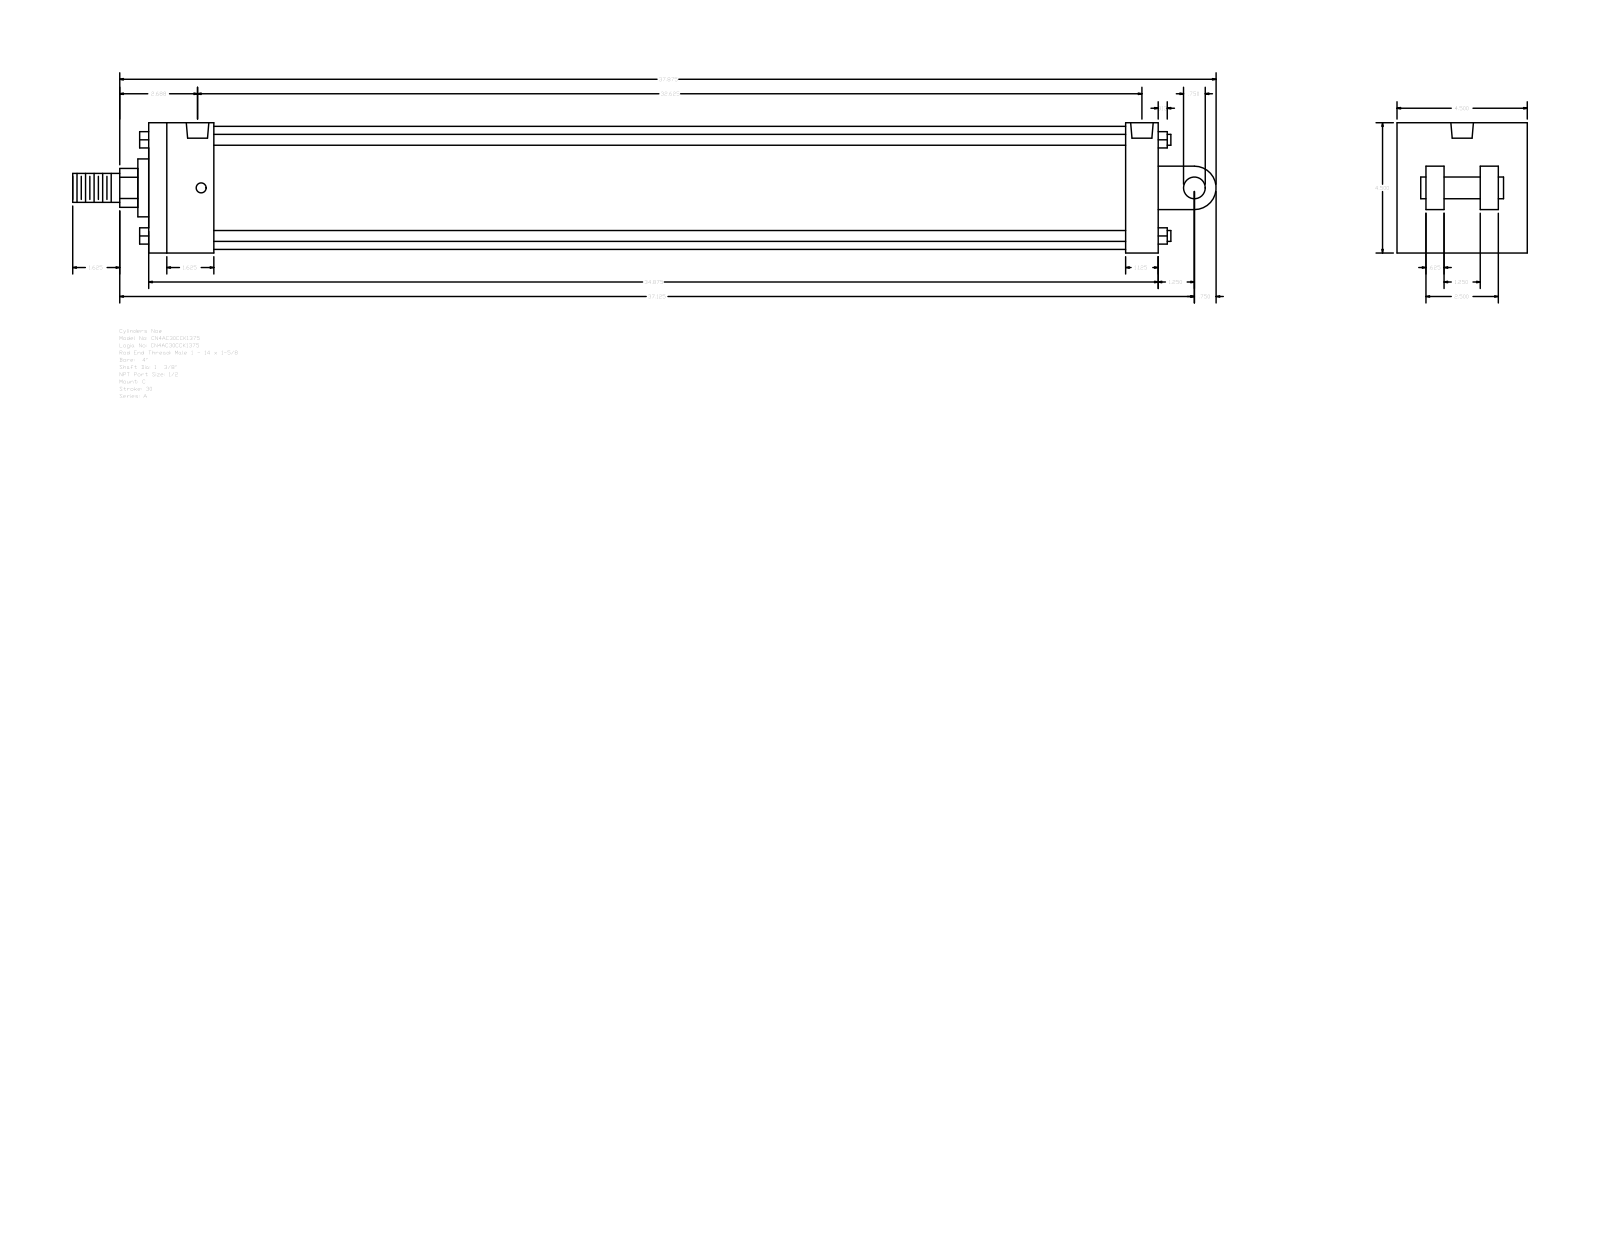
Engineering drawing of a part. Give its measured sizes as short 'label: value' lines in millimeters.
name: A_C__0400_1.375
written by: GSSL Pune (CONFIG_CONTROL_DESIGN)
unit: mm
bodies: 0 solids, 135 faces (102 planar, 33 cylindrical, 0 other)
size: 1003.3 × 114.3 × 114.3
holes: 4× ⌀8.73, 2× ⌀19.77
bosses: 4× ⌀9.53, 1× ⌀107.95, 1× ⌀50.8, 1× ⌀34.92, 1× ⌀25.4, 1× ⌀19.05
rounds: 1× R17.06, 1× R19.05
face distances: 114.3, 885.83, 57.15, 28.58, 73.03, 857.25, 800.1, 828.68, 41.27, 25.4
hole spacings: 3.18, 822.32, 825.5, 828.68
